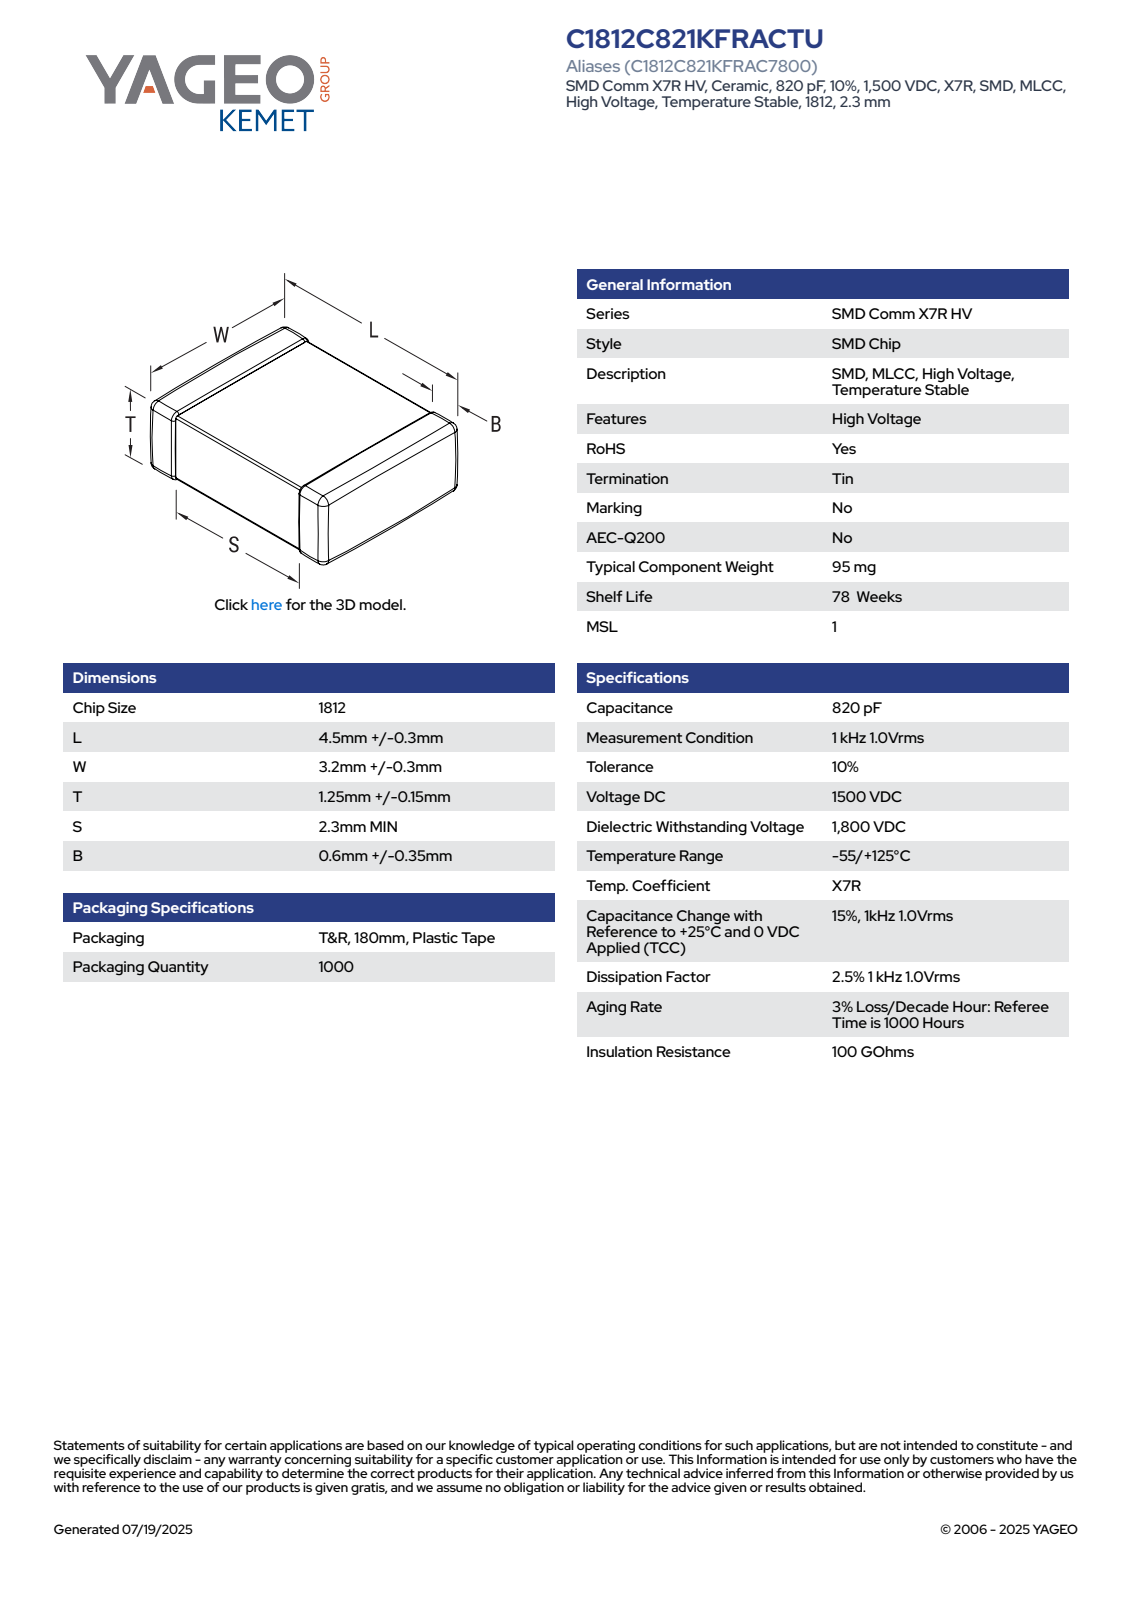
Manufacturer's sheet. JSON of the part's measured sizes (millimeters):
{"part_name": "CCS_CCSTD_1812_L4.8W3.5T1.4B0.6", "step_written_by": "SolidWorks 2021 (AUTOMOTIVE_DESIGN)", "units": "millimeters", "bodies": {"solids": 4, "faces": 129, "planar": 71, "cylindrical": 42, "other": 16}, "overall_size": [4.8, 3.5, 1.4], "volume_mm3": 21, "surface_area_mm2": 56, "face_to_face_distances": [1.33, 1.26, 1.4, 4.8, 3.43, 3.36, 3.5, 2.08, 2.72, 2.59]}
